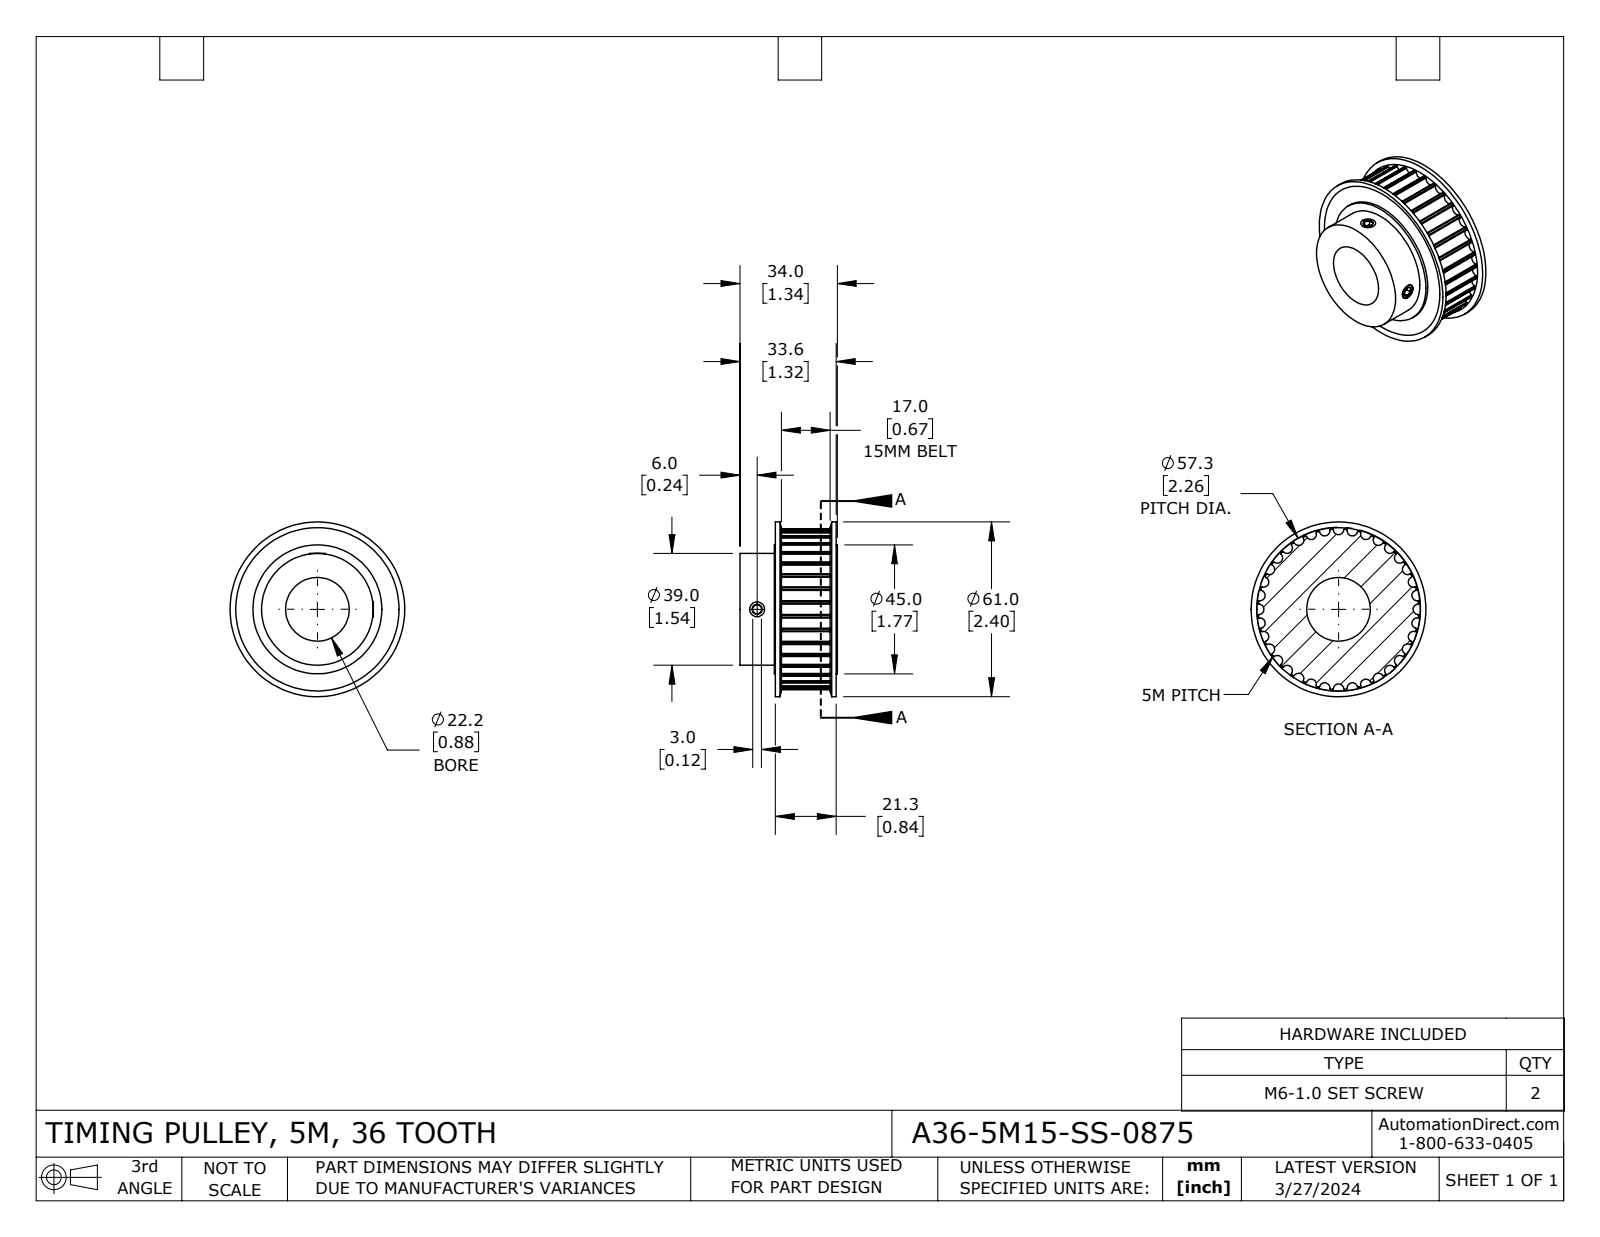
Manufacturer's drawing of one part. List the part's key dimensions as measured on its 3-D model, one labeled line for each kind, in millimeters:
Part name (STEP PRODUCT): A36-5M15-SS-0875
STEP written by: SolidWorks 2021 (CONFIG_CONTROL_DESIGN)
Units: millimetres
Bodies: 5 solids, 262 faces (25 planar, 203 cylindrical, 34 other)
Overall size (bounding box): 61 × 61 × 34
Volume: 51 741 mm³ · Surface area: 19 510 mm²
Round holes (diameter × count): ⌀5 ×2, ⌀22.23 ×1, ⌀45 ×1
Round bosses / shafts (diameter × count): ⌀6 ×2, ⌀61 ×1, ⌀39 ×1
Partial cylindrical surfaces — rounded edges, fillets, slot ends (radius × count): R0.3 ×72, R1.82 ×36, R28.07 ×1
Main face-to-face distances: 1.6, 18.6, 17, 2.5, 19.5, 0.9, 21.1, 20.2, 34, 33.1
